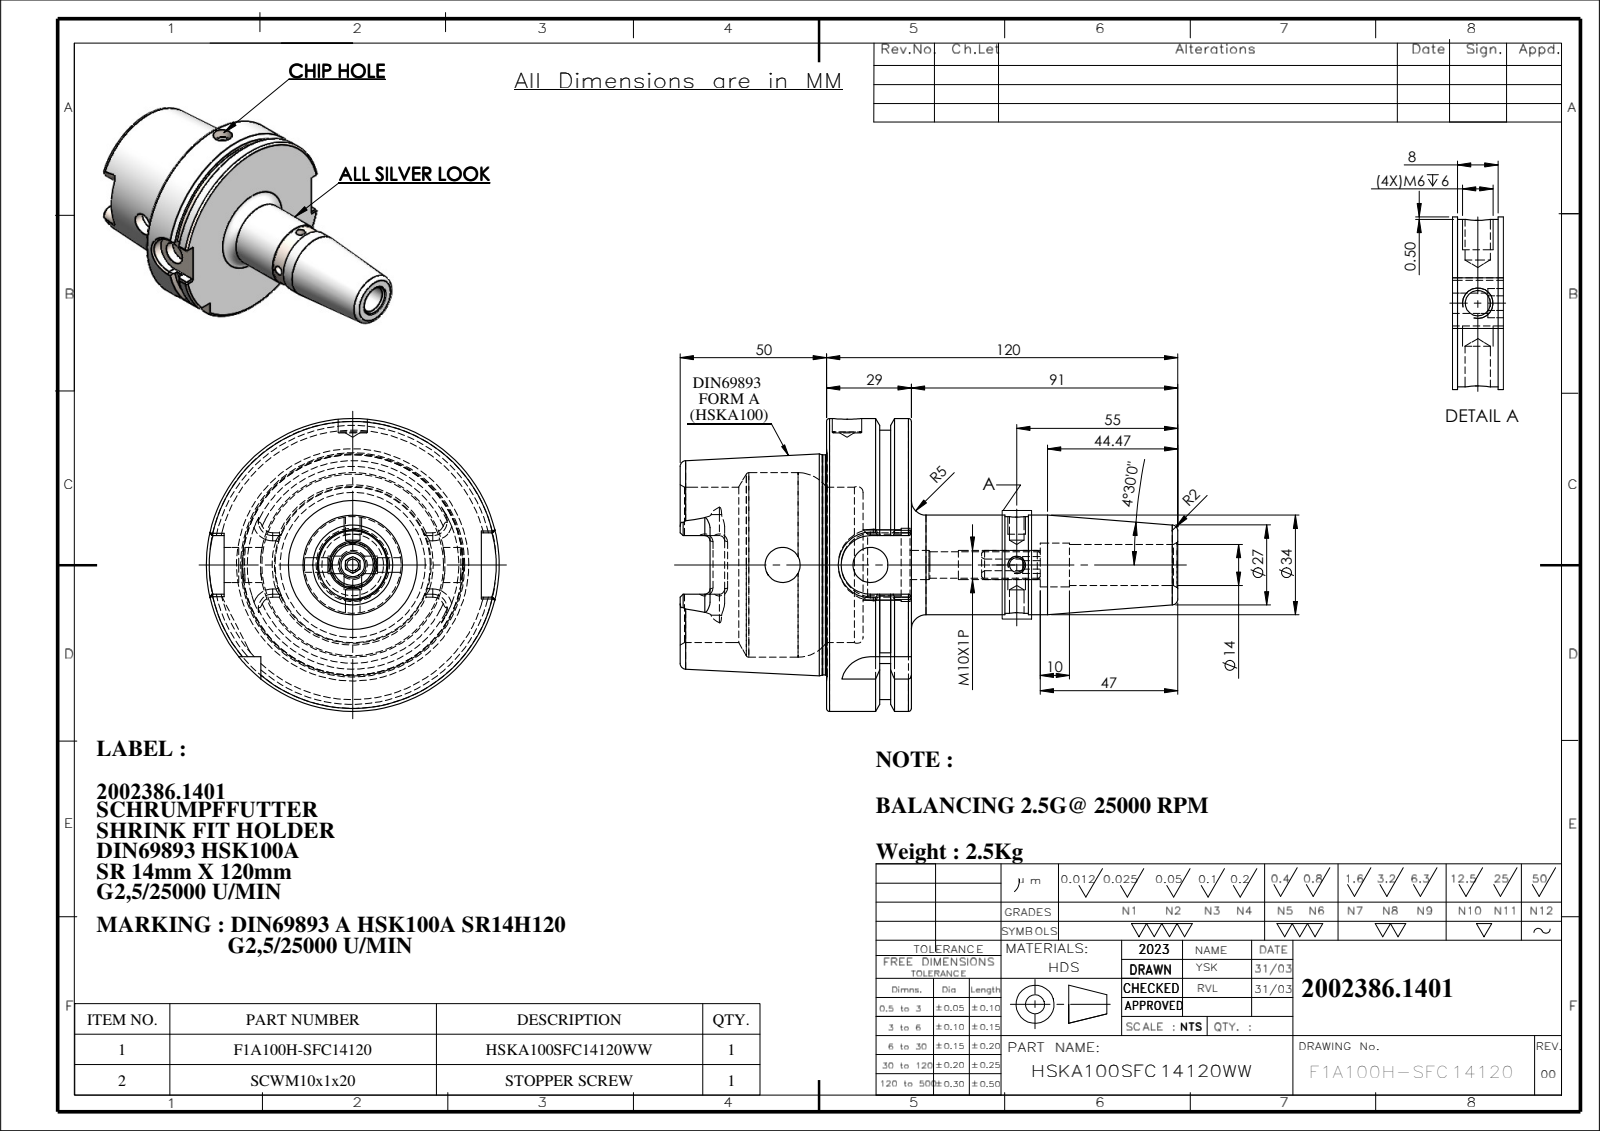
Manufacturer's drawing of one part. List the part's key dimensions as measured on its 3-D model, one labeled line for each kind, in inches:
Part name (STEP PRODUCT): 91100A-SR14120; HSKA100SFC14120WW; SCWM10X1
STEP written by: SolidWorks 2018 (CONFIG_CONTROL_DESIGN)
Units: inches
Bodies: 2 solids, 222 faces (64 planar, 70 cylindrical, 88 other)
Overall size (bounding box): 6.691 × 3.937 × 3.937
Volume: 19.46 in³ · Surface area: 98.22 in²
Round holes (diameter × count): ⌀0.197 ×2, ⌀0.394 ×2, ⌀0.472 ×2, ⌀0.157 ×1, ⌀0.354 ×1, ⌀0.55 ×1, ⌀0.59 ×1, ⌀0.827 ×1, ⌀0.984 ×1, ⌀2.087 ×1, ⌀2.48 ×1
Round bosses / shafts (diameter × count): ⌀3.937 ×1, ⌀3.622 ×1, ⌀2.959 ×1, ⌀1.339 ×1, ⌀1.299 ×1
Partial cylindrical surfaces — rounded edges, fillets, slot ends (radius × count): R0.071 ×6, R0.192 ×4, R0.394 ×2, R0.433 ×1
Main face-to-face distances: 1.14, 0.492, 0.648, 1.969, 2.461, 3.108, 0.63, 3.091, 1.122, 0.018
Hole centre spacings: 1.181, 1.967, 2.281, 3.148
